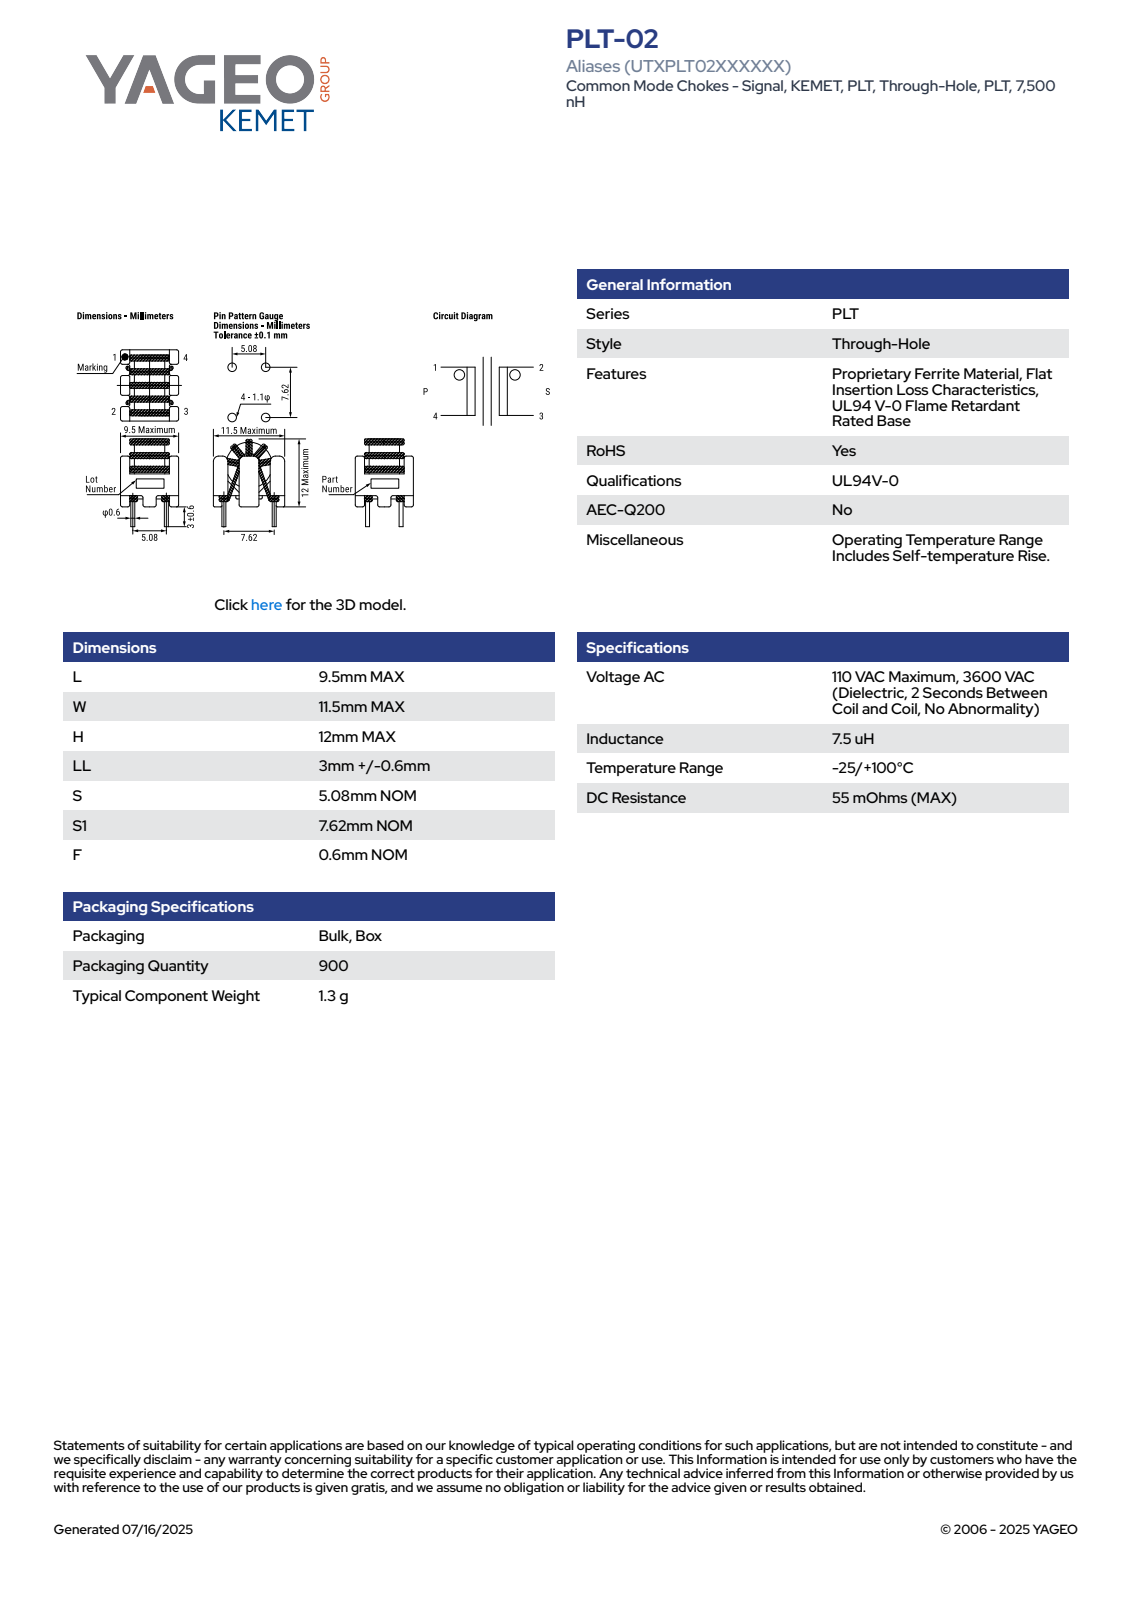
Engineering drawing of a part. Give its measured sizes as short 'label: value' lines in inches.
name: PT_KPLT02_L9.5W11.5H12LL3.6S5.08
written by: SolidWorks 2014 (AUTOMOTIVE_DESIGN)
unit: in
bodies: 2 solids, 607 faces (220 planar, 227 cylindrical, 160 other)
size: 0.614 × 0.453 × 0.374
volume: 0.034 in³; area: 1.877 in²
holes: 1× ⌀0.161
bosses: 4× ⌀0.024
rounds: 78× R0.009, 36× R0.008, 12× R0.012, 10× R0.02, 1× R0.156
face distances: 0.057, 0.317, 0.019, 0.374, 0.26, 0.146, 0.307, 0.453, 0.081, 0.065
